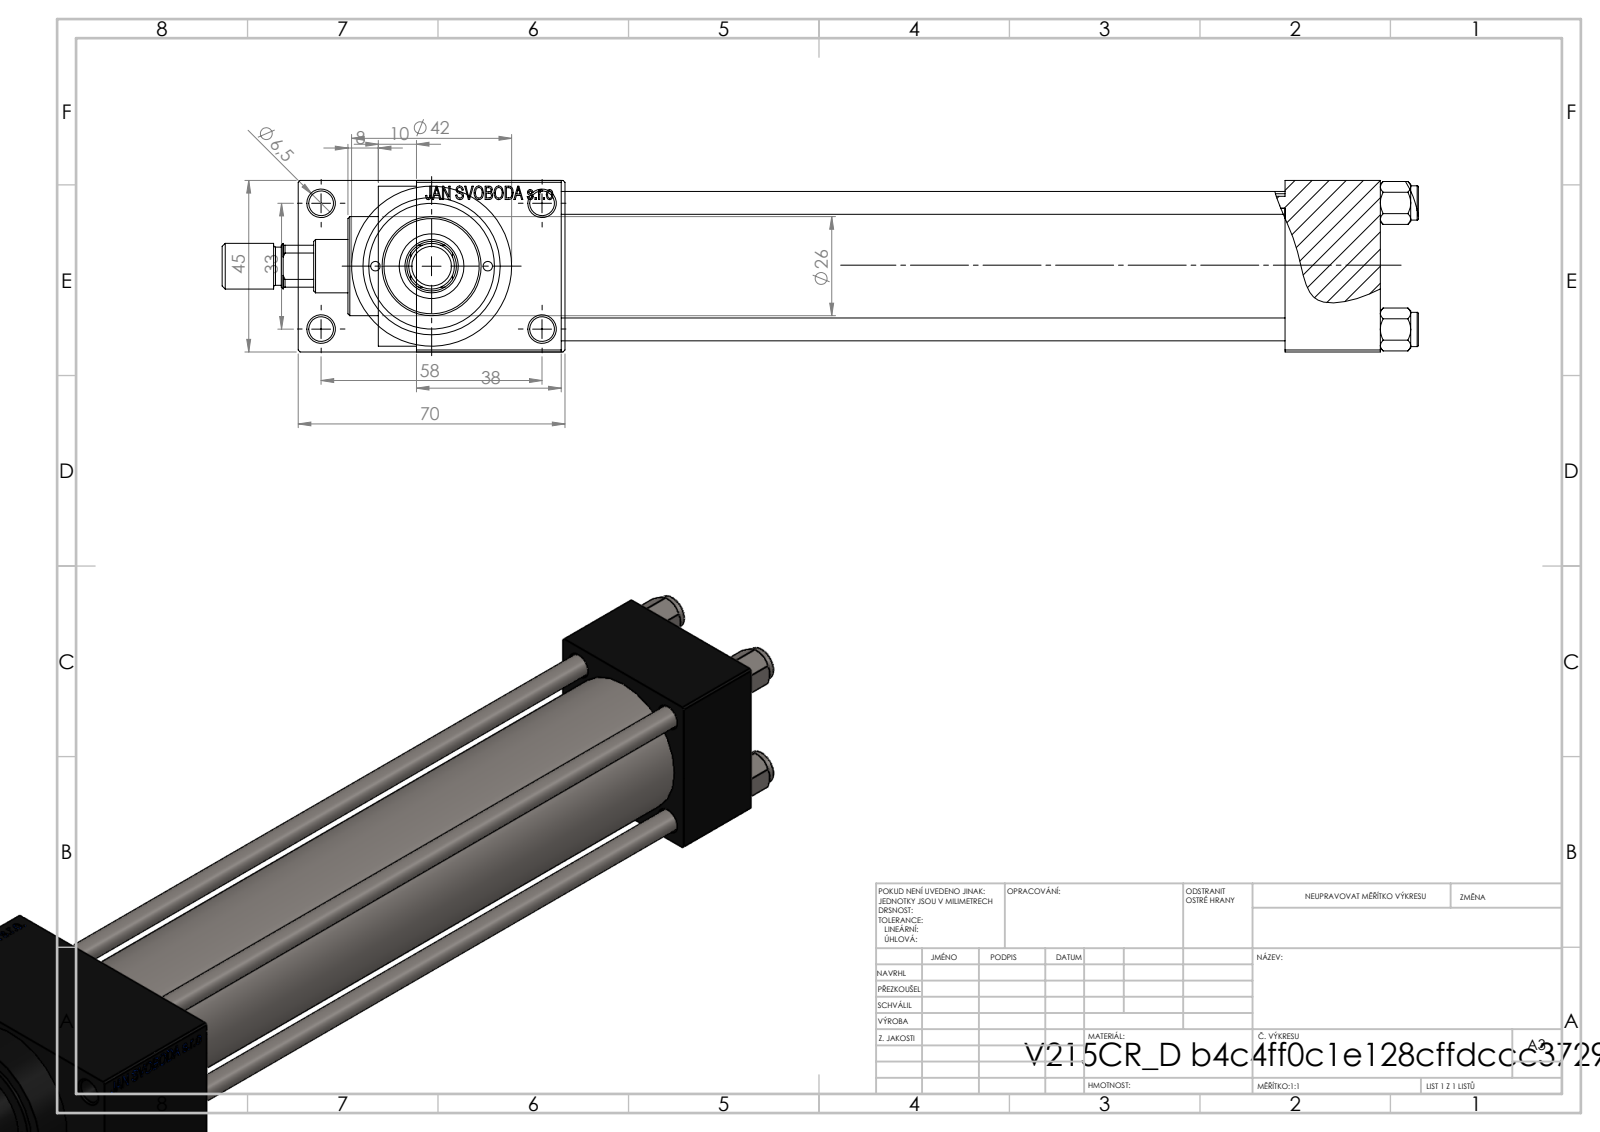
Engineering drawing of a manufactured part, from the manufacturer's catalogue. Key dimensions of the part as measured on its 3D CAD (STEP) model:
Part name (STEP PRODUCT): NUT_M5_D; V215CR_D_Body; V215CR_D_TYCINKA; V215CR_VCP_D (+2 more)
STEP written by: SolidWorks 2019 (CONFIG_CONTROL_DESIGN)
Units: millimetres
Bodies: 12 solids, 1124 faces (502 planar, 96 cylindrical, 526 other)
Overall size (bounding box): 314 × 70 × 45
Volume: 315 450 mm³ · Surface area: 123 729 mm²
Round holes (diameter × count): ⌀6.5 ×5, ⌀6 ×4, ⌀2.5 ×2, ⌀7 ×2, ⌀13.16 ×2, ⌀20 ×2, ⌀14 ×1, ⌀17 ×1, ⌀24 ×1, ⌀32 ×1, ⌀33 ×1
Round bosses / shafts (diameter × count): ⌀9 ×4, ⌀42 ×1, ⌀38 ×1, ⌀26 ×1, ⌀12 ×1, ⌀10 ×1
Partial cylindrical surfaces — rounded edges, fillets, slot ends (radius × count): R6.5 ×1
Main face-to-face distances: 45, 25, 12.5, 190, 215, 57.5, 228, 38, 253, 70
Hole centre spacings: 12.4, 16.7, 21.8, 23.48, 33.2, 33.37, 35.35, 35.47
